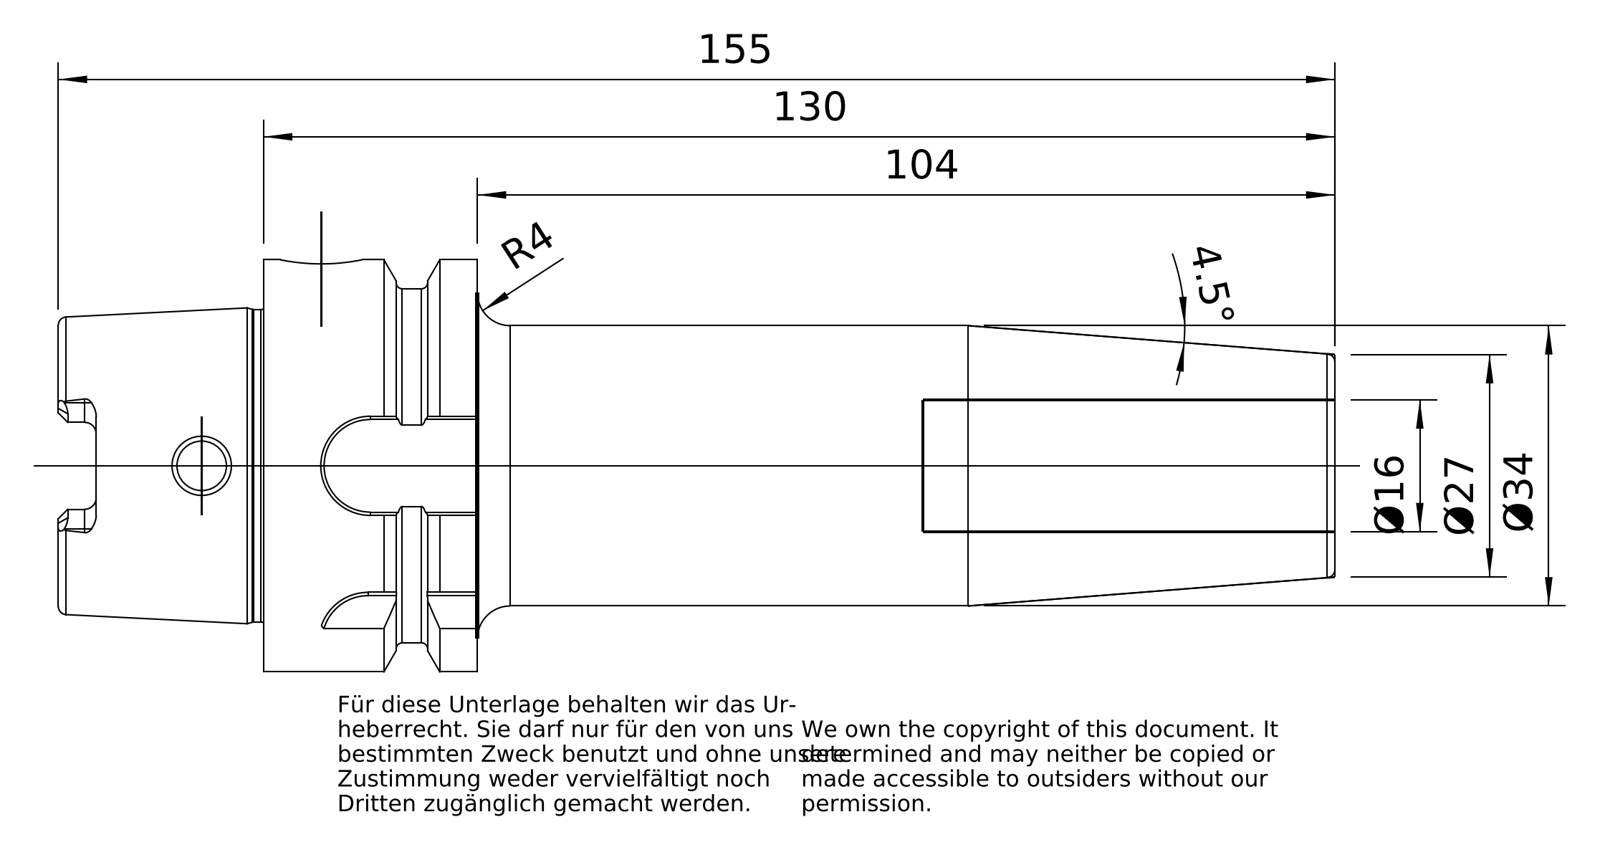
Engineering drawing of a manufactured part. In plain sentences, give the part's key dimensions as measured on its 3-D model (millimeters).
The part is named "A50-144-16". Its 3-D file was written by "PRO/ENGINEER BY PARAMETRIC TECHNOLOGY CORPORATION, 2010430 (CONFIG_CONTROL_DESIGN)". It is 1 solid with 185 faces: 64 planar, 49 cylindrical and 72 other. Overall it measures 154.9 by 50 by 50 millimeters. Its volume is 125 912 cubic millimeters and its surface area 27 920 square millimeters. Round holes: 1 of diameter 6, 1 of diameter 10, 1 of diameter 14, 1 of diameter 16, 1 of diameter 16.32, 1 of diameter 16.5, 1 of diameter 26.04, 1 of diameter 32.08. Round bosses or shafts: 1 of diameter 50, 1 of diameter 42.95, 1 of diameter 37.91, 1 of diameter 34. Partial cylindrical surfaces (rounded edges, fillets, slot ends): 6 of radius 1.4, 4 of radius 2.38, 3 of radius 6, 1 of radius 6.02. The main face-to-face distances are 25.95, 130, 104.05, 24.9, 50.85, 154.9, 34.85, 9.95, 16, 120.05.
